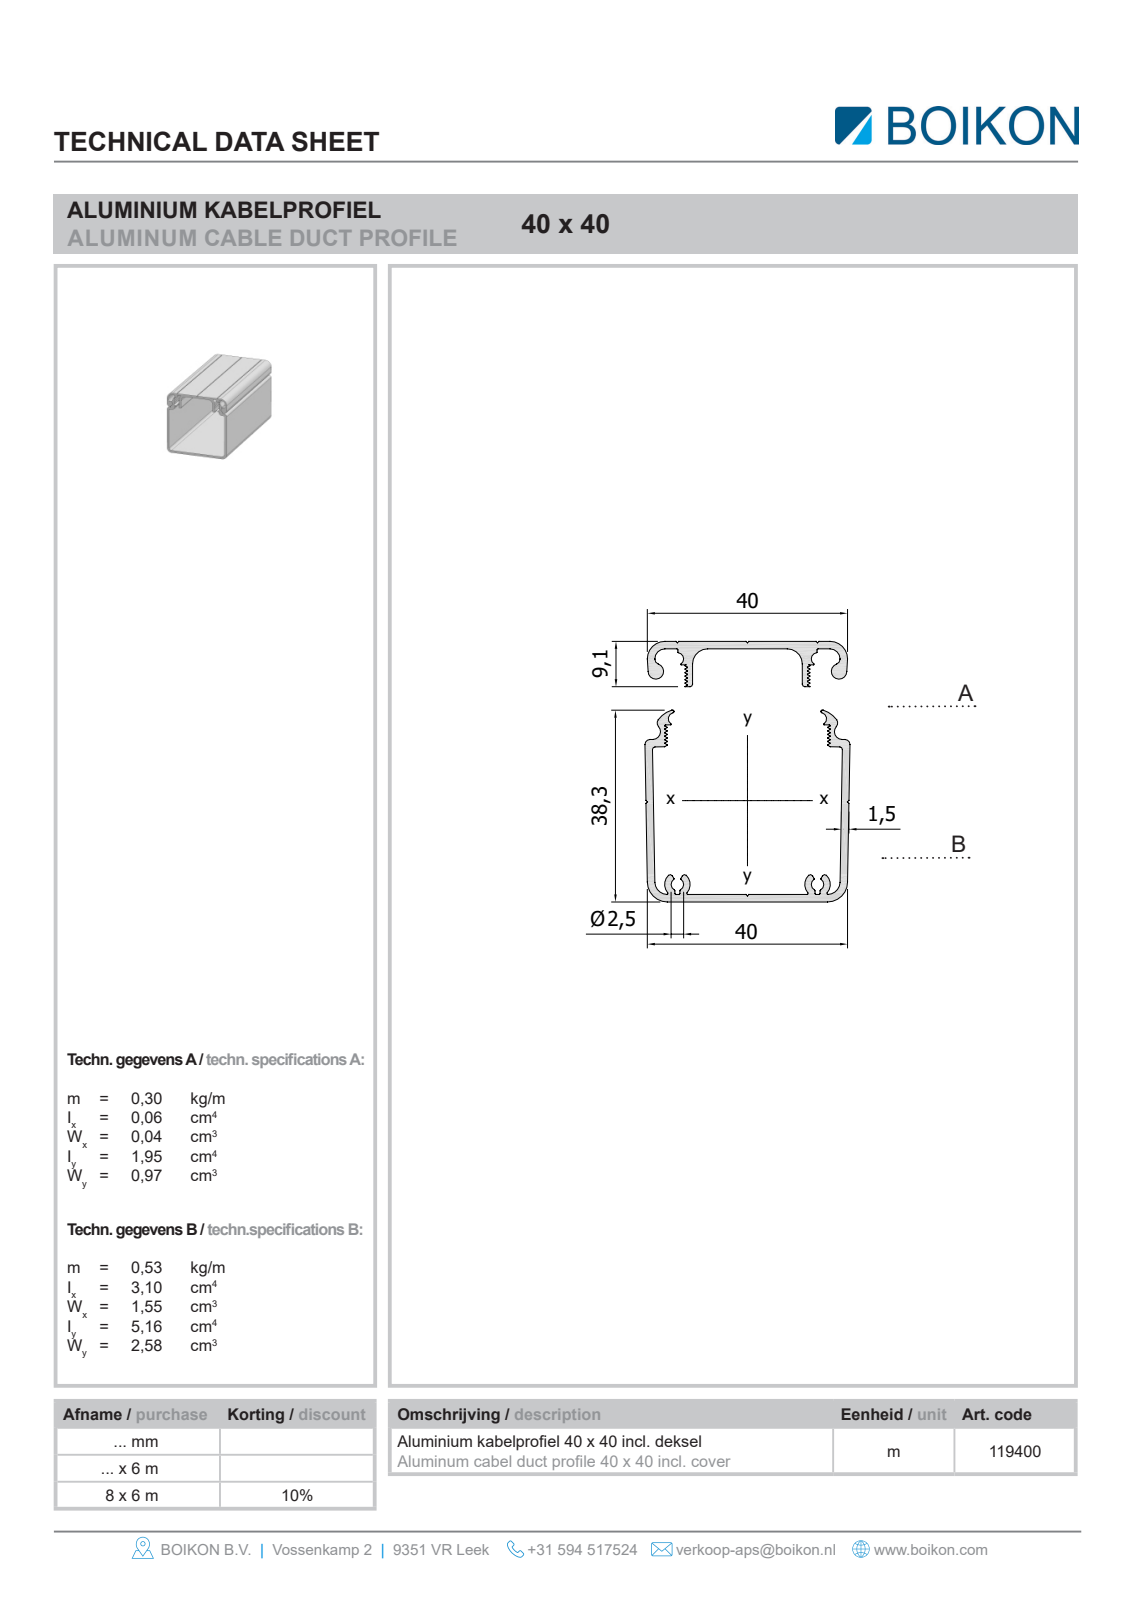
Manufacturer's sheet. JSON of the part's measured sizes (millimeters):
{"part_name": "Root; 119400Kabelgootprofiel 40x40BOIKON0", "step_written_by": "HiCAD 2013 1802.4 Build 509 (AUTOMOTIVE_DESIGN)", "units": "millimeters", "bodies": {"solids": 2, "faces": 185, "planar": 107, "cylindrical": 78, "other": 0}, "overall_size": [1000, 40.02, 40], "volume_mm3": 284579, "surface_area_mm2": 393115, "partial_cylinders_radius": [[0.12, 22], [0.5, 16], [3, 6], [1.5, 4], [2, 4], [0.25, 2], [0.8, 2], [0.81, 2]], "face_to_face_distances": [1.5, 38.5, 40, 37, 1, 9.5, 30.5, 8.03, 30.53, 30.47]}
